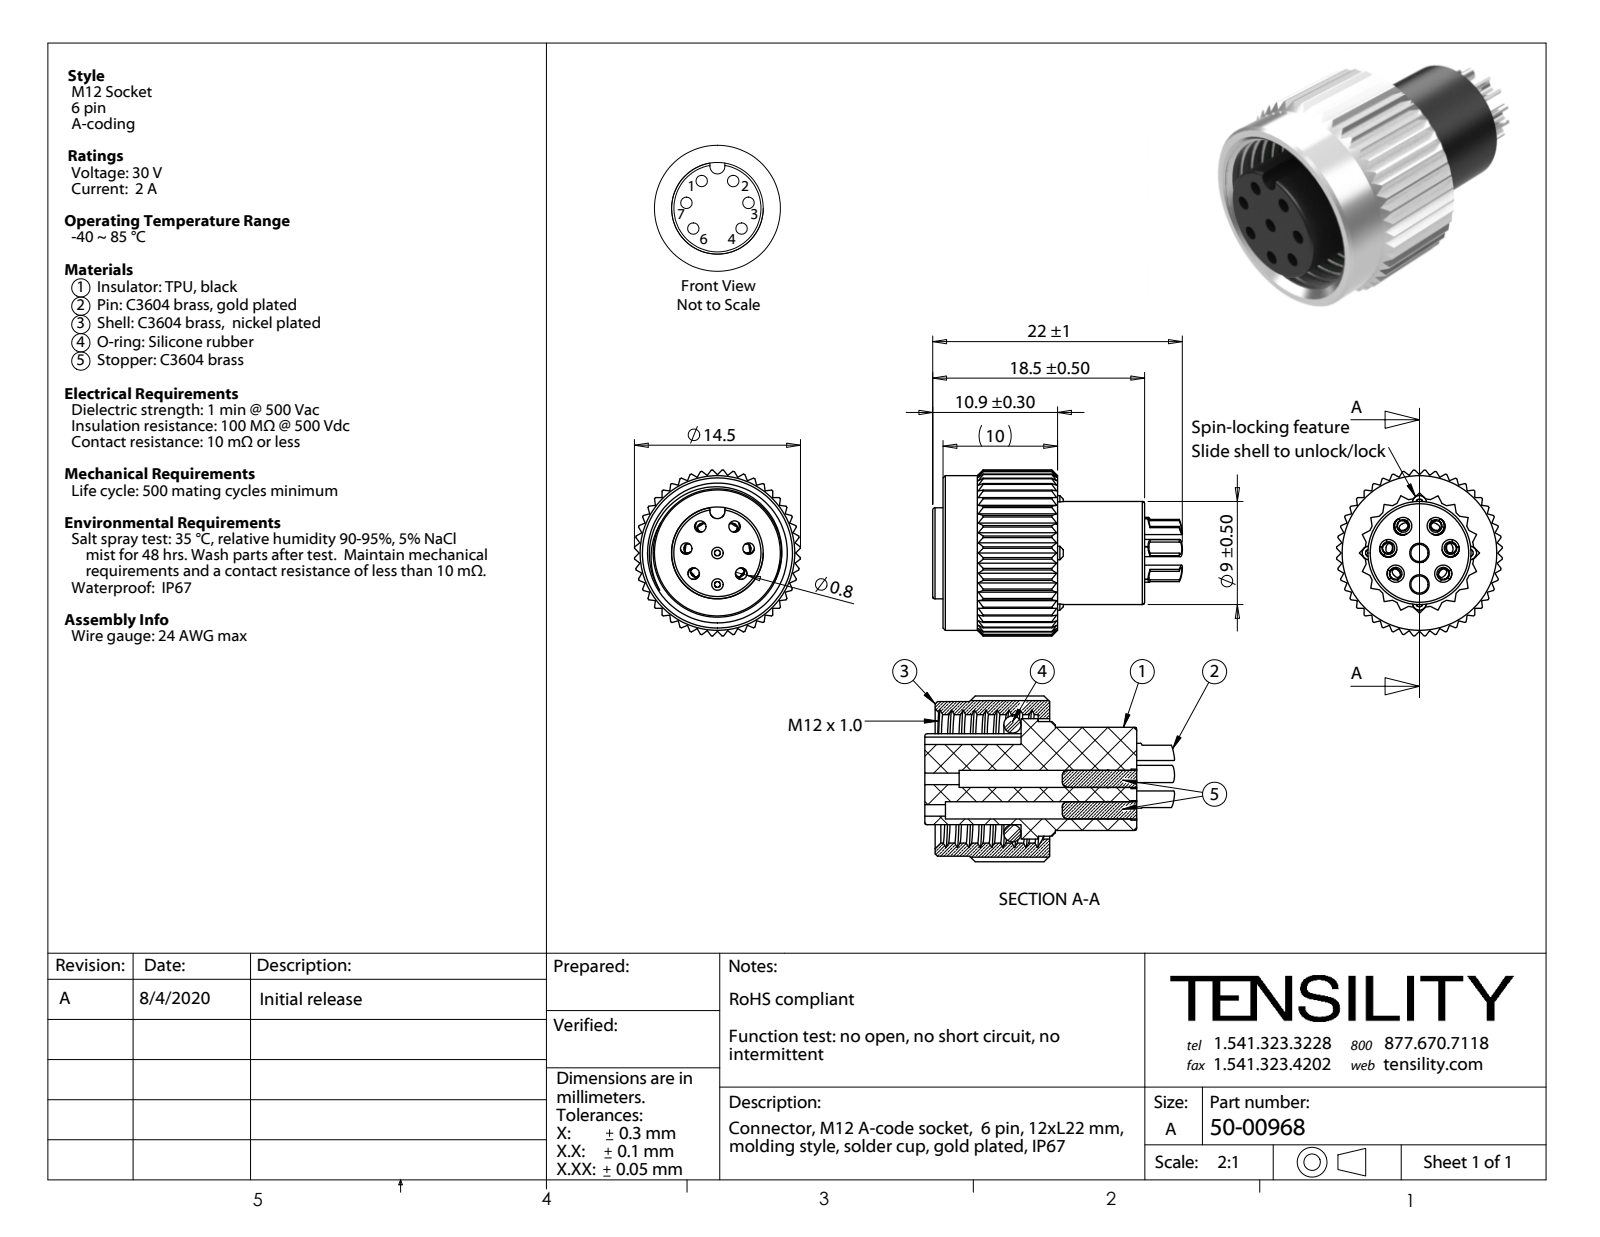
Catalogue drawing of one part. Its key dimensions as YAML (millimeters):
part_name: "50-00968-03; 50-00968-01; 50-00968-04; 50-00968 (+2 more)"
step_written_by: "SolidWorks 2021 (CONFIG_CONTROL_DESIGN)"
units: millimeters
bodies: {solids: 11, faces: 873, planar: 328, cylindrical: 296, other: 249}
overall_size: [21.8, 14.48, 14.48]
volume: 1530
surface_area: 3695
round_holes:
  - {diameter: 1, count: 8}
  - {diameter: 1.1, count: 6}
  - {diameter: 1.2, count: 6}
  - {diameter: 1.5, count: 4}
  - {diameter: 11.2, count: 1}
round_bosses_or_shafts:
  - {diameter: 1.5, count: 8}
  - {diameter: 1.6, count: 6}
  - {diameter: 1.7, count: 2}
  - {diameter: 13.5, count: 1}
  - {diameter: 10.5, count: 1}
  - {diameter: 9, count: 1}
  - {diameter: 8, count: 1}
partial_cylinders:
  - {radius: 0.1, count: 12}
  - {radius: 0.4, count: 12}
  - {radius: 0.6, count: 4}
  - {radius: 0.65, count: 1}
  - {radius: 4.75, count: 1}
  - {radius: 7.25, count: 1}
face_to_face_distances: [9.66, 7.6, 10.9, 18.5, 2.5, 8.4, 10.1, 1.5, 9.9, 1]
hole_center_spacings: [2.75, 5.44, 4.15, 2.24, 2.27, 2.28, 2.29, 2.32]
